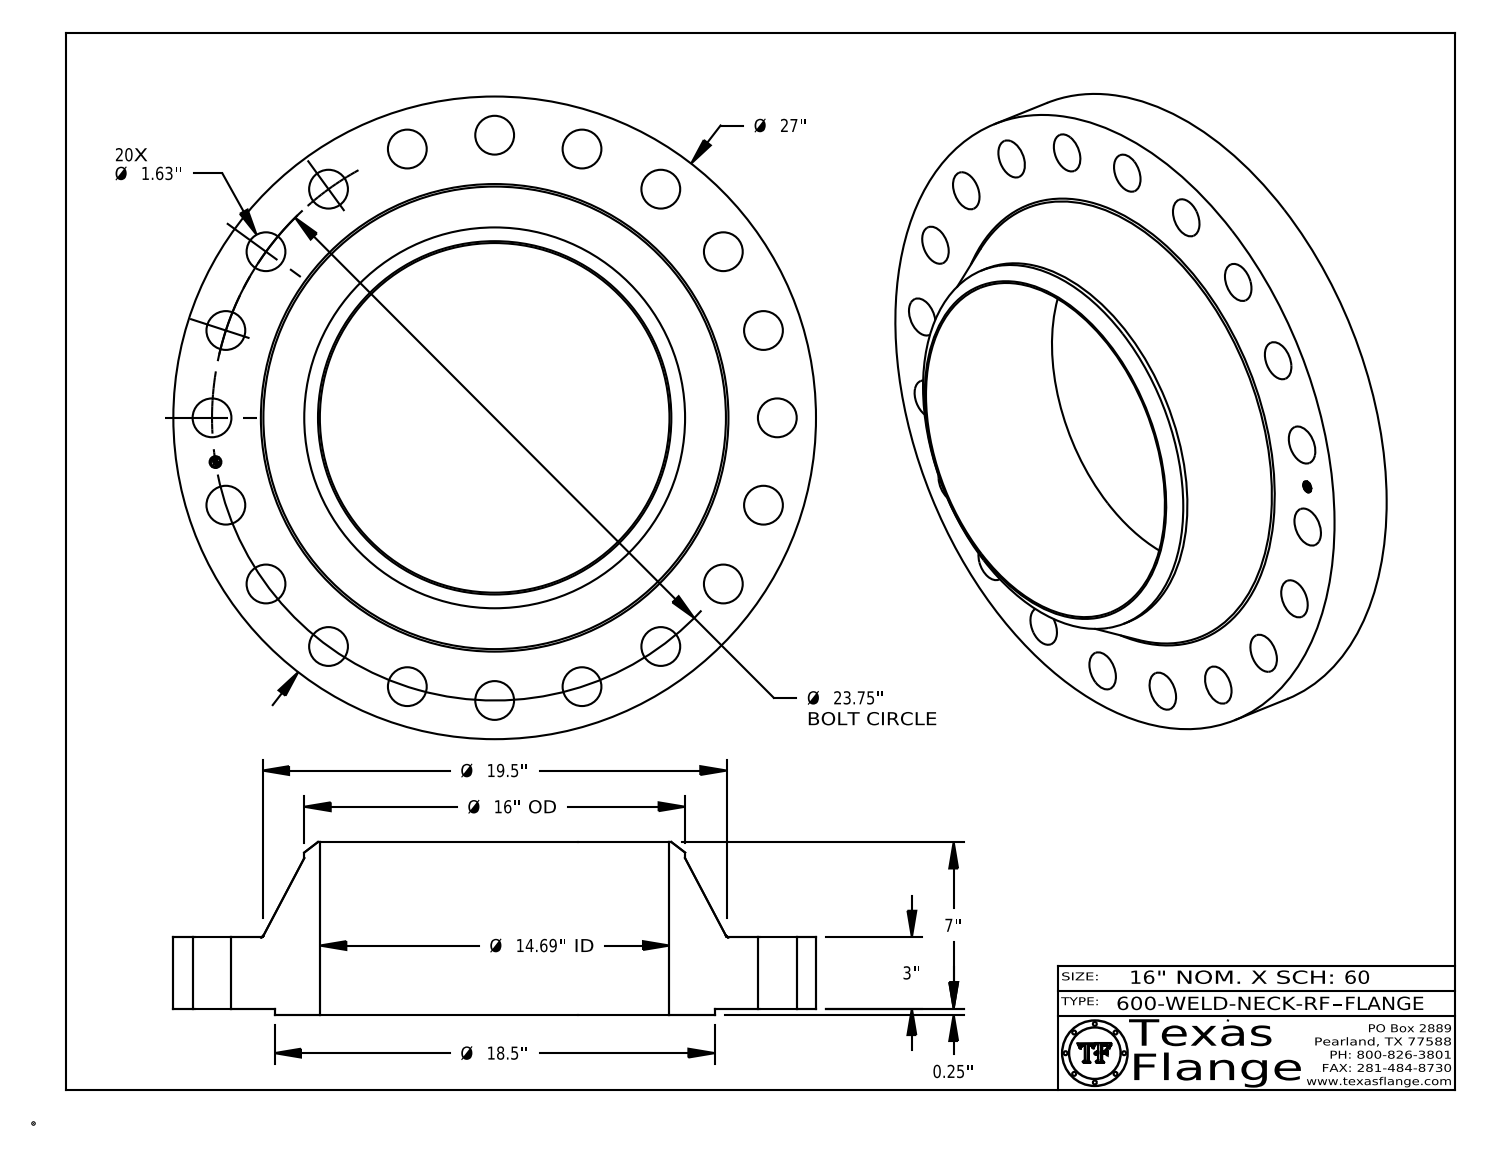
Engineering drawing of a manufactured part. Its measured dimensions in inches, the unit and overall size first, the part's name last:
Units: inches
Overall size (bounding box): 27 × 27 × 7.25
Round holes (diameter × count): ⌀1.63 ×20, ⌀0.495 ×1, ⌀14.688 ×1
Round bosses / shafts (diameter × count): ⌀0.03 ×8, ⌀27 ×1, ⌀18.5 ×1, ⌀16 ×1, ⌀0.39 ×1
Main face-to-face distances: 3, 0.25, 3.25, 7.25, 7, 4, 3.235, 2.985, 0.015, 4.015
Hole centre spacings: 11.875, 16.794, 19.214, 22.587, 23.457, 7.339, 10.782, 3.715
Volume: 1 386 in³ · Surface area: 1 764 in²
Bodies: 1 solid, 443 faces (369 planar, 68 cylindrical, 6 other)
Part name (STEP PRODUCT): 600-WELD-NECK-RF
STEP written by: CATIA V5 STEP AP214 (AUTOMOTIVE_DESIGN)
